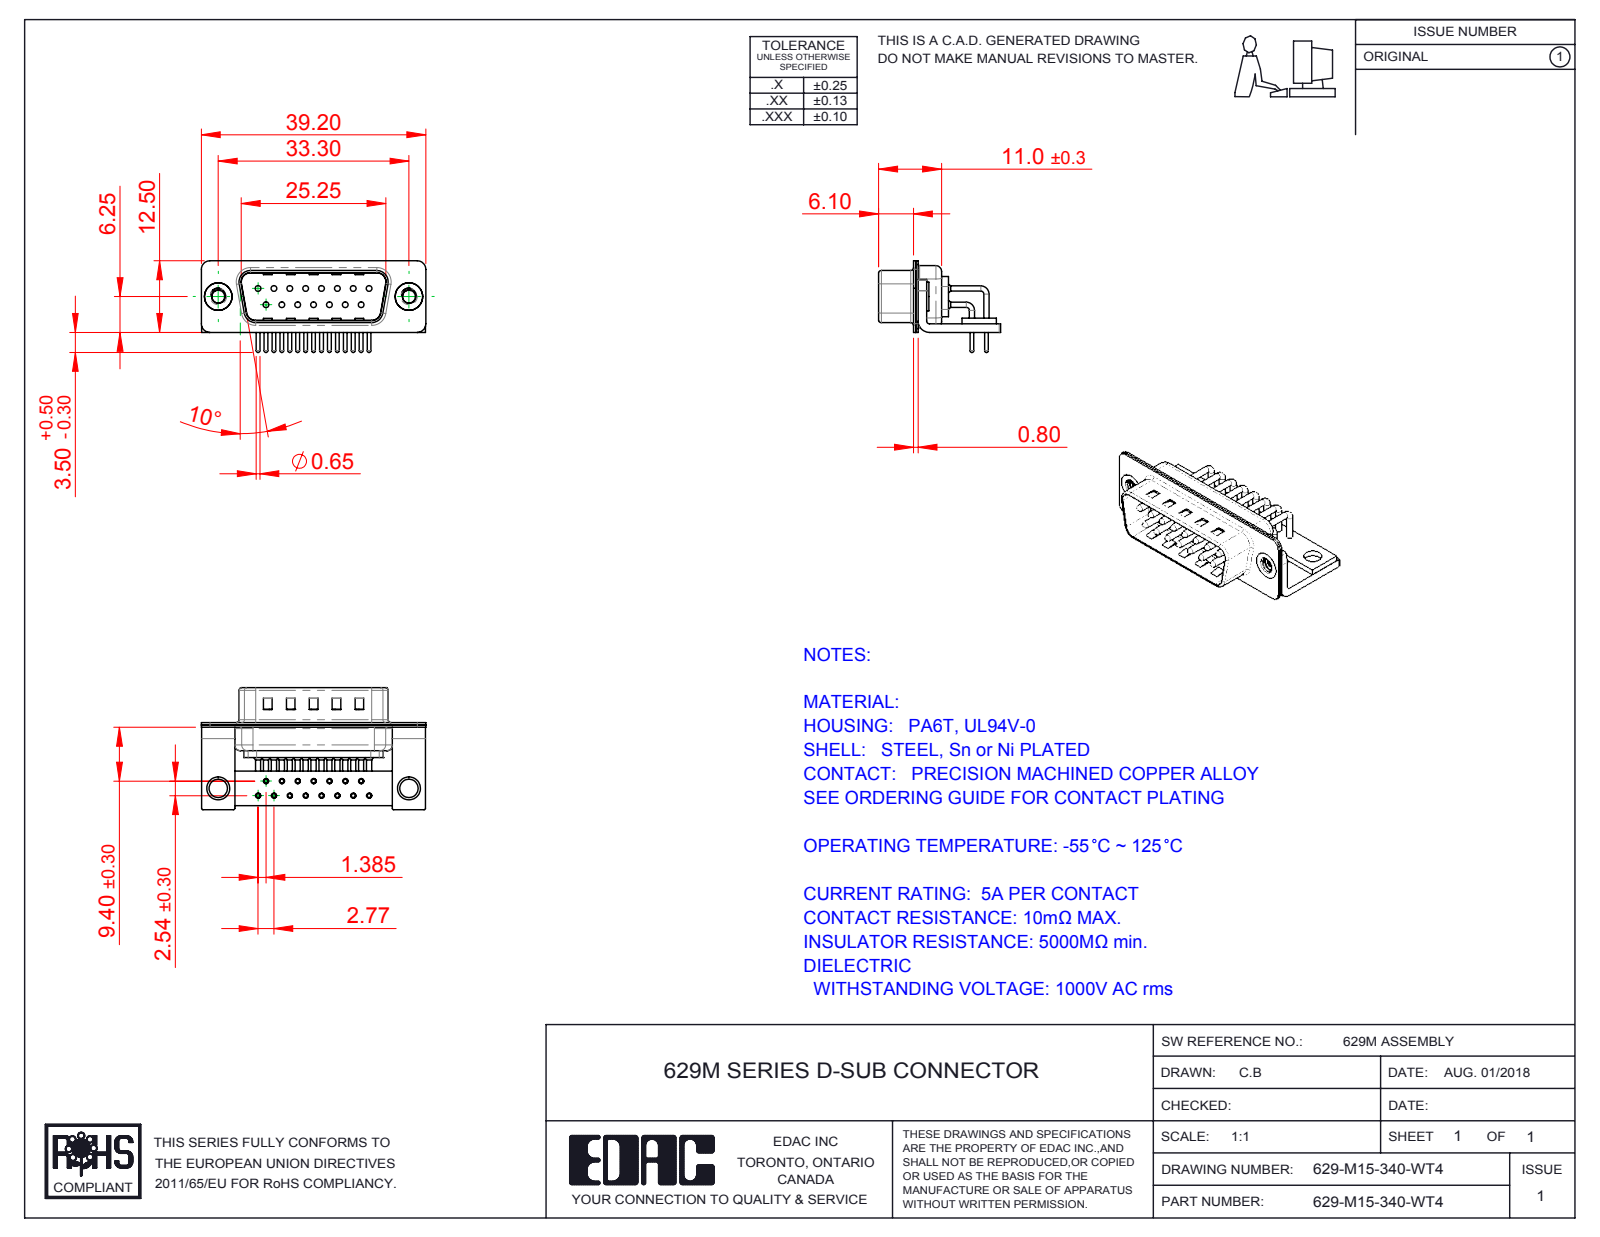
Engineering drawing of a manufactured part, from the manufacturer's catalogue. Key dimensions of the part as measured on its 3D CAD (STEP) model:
Part name (STEP PRODUCT): 629M Contact Row 2; 629-M15-340-WT4; 629M Housing_15 Contacts; 629M Shell Front_15 Contacts (+5 more)
STEP written by: SolidWorks 2016 (CONFIG_CONTROL_DESIGN)
Units: millimetres
Bodies: 23 solids, 2070 faces (1125 planar, 725 cylindrical, 220 other)
Overall size (bounding box): 39.2 × 21.3 × 16
Volume: 2 435 mm³ · Surface area: 6 519 mm²
Round holes (diameter × count): ⌀0.9 ×15, ⌀1 ×15, ⌀1.7 ×15, ⌀2 ×15, ⌀2.26 ×2, ⌀3.2 ×2, ⌀4 ×2, ⌀4.8 ×2
Round bosses / shafts (diameter × count): ⌀0.9 ×21, ⌀1.5 ×15, ⌀0.65 ×15, ⌀5 ×2, ⌀4.9 ×2
Partial cylindrical surfaces — rounded edges, fillets, slot ends (radius × count): R0.25 ×16, R1.5 ×16, R1.01 ×15, R2 ×13, R0.5 ×9, R1.6 ×8, R0.6 ×4, R0.65 ×4
Main face-to-face distances: 0.4, 1.5, 0.85, 0.8, 1.25, 10.4, 9.55, 1.9, 1, 8.3
Hole centre spacings: 2.77, 5.54, 3.16, 8.31, 4.87, 11.08, 2.89, 7.37
